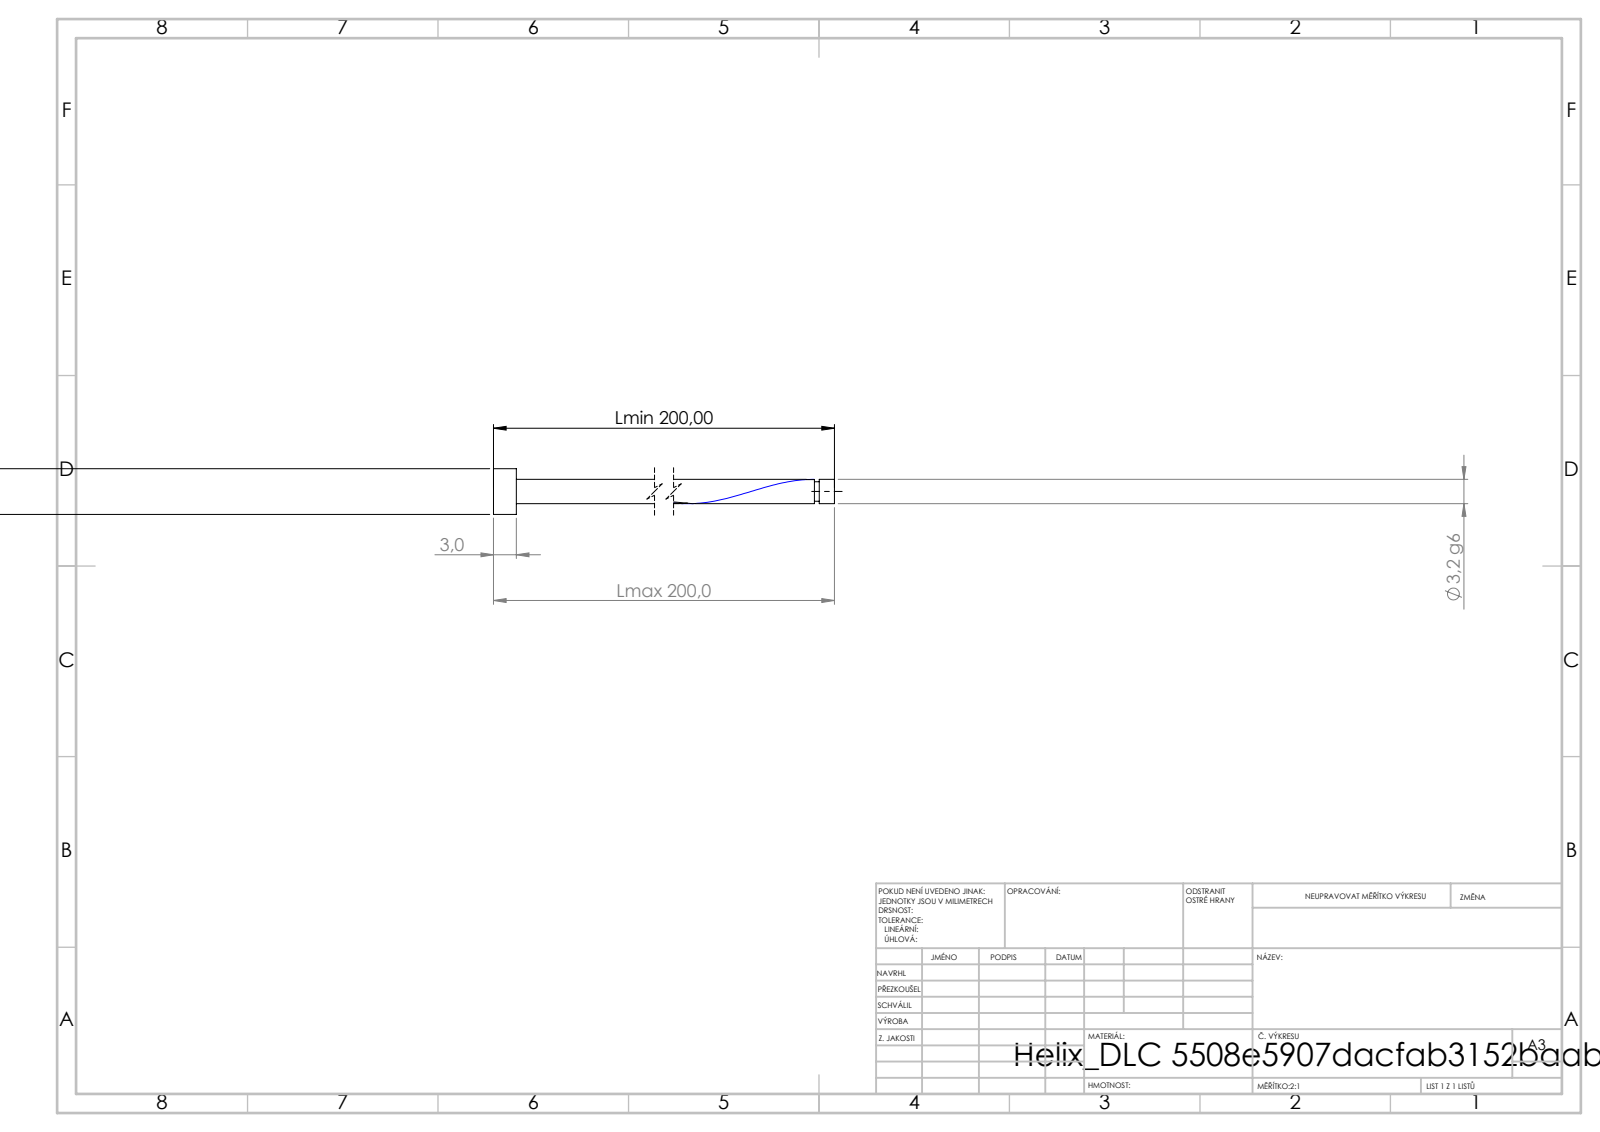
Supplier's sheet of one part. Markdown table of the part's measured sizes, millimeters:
| quantity | value |
| --- | --- |
| STEP written by | SolidWorks 2019 (CONFIG_CONTROL_DESIGN) |
| units | millimeters |
| bodies | 1 solid, 16 faces (6 planar, 9 cylindrical, 1 other) |
| overall size | 200 × 6 × 6 |
| volume | 2 010 mm³ |
| surface area | 2 801 mm² |
| round bosses / shafts (diameter × count) | 6 × 1, 3.2 × 1, 2.56 × 1 |
| main face-to-face distances | 3, 200, 197, 198.01, 195.01, 1.99, 197.37, 194.37, 0.64, 2.63 |
